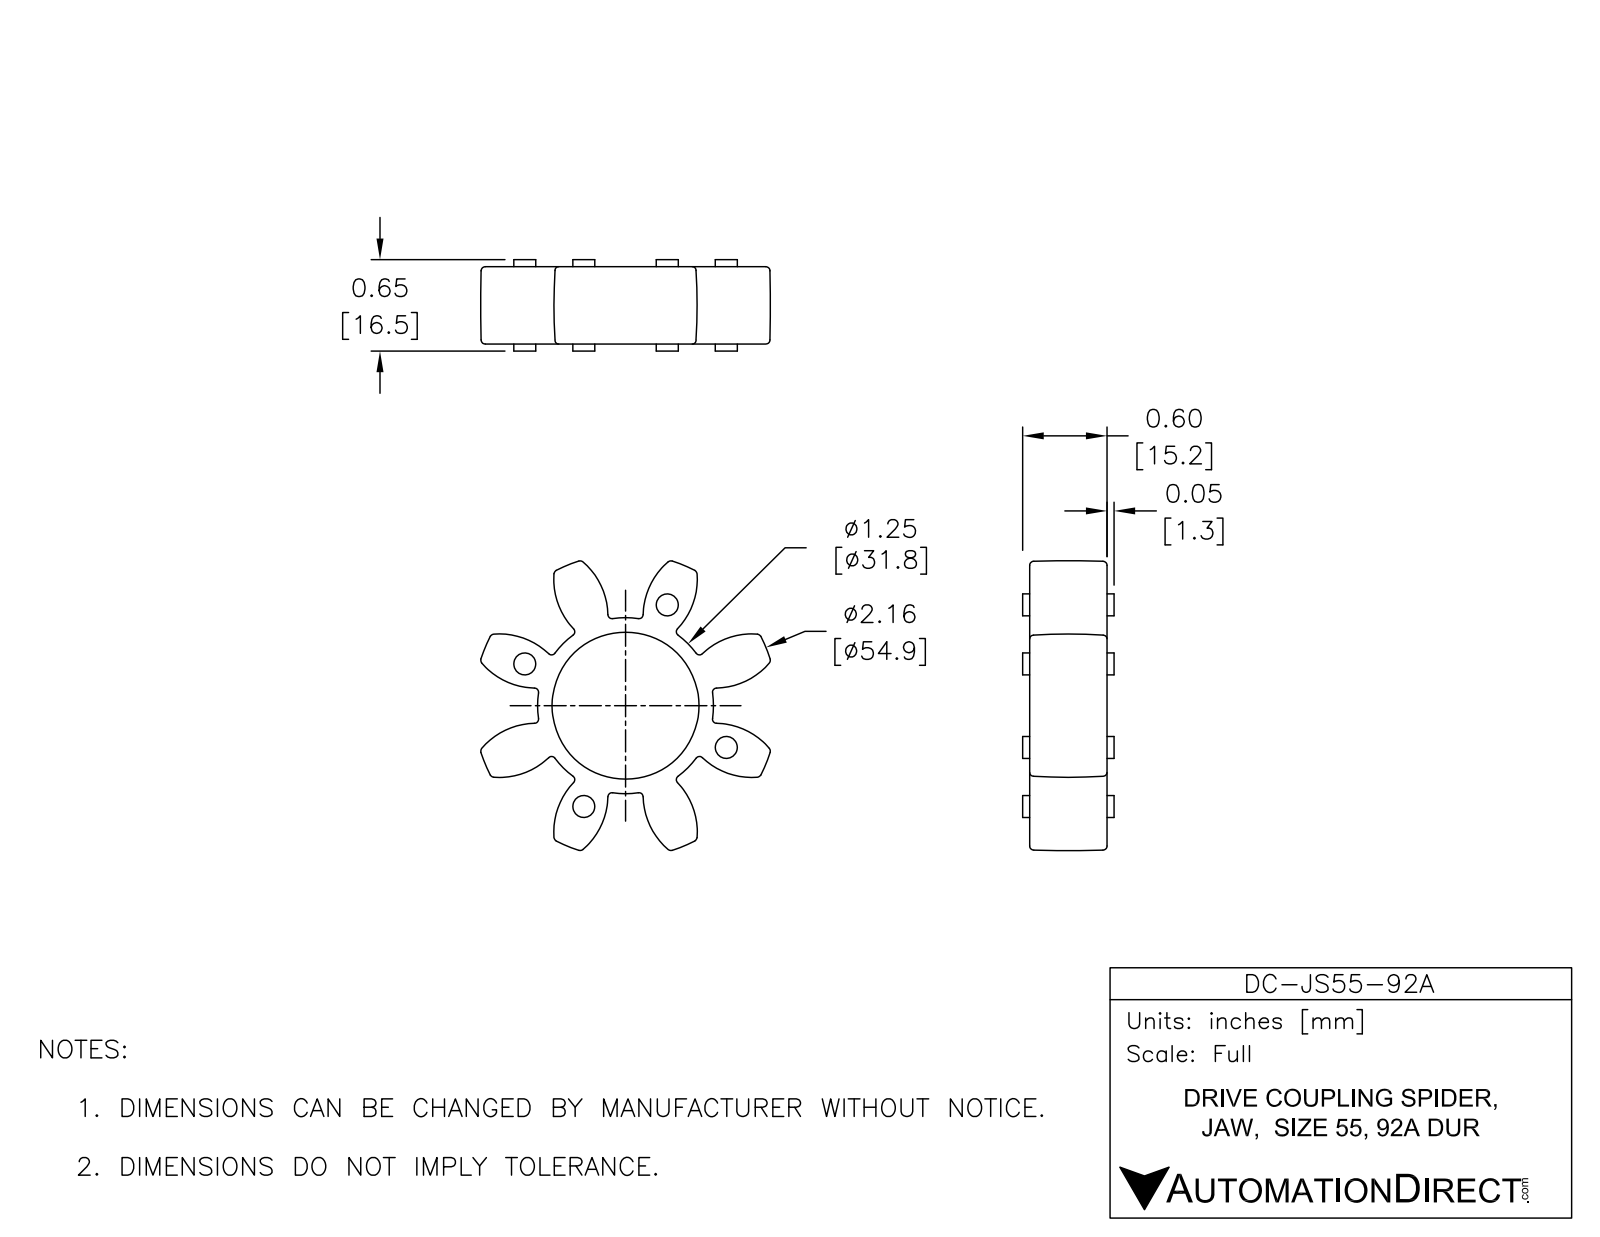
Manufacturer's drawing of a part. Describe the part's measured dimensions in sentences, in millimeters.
The part is named "DC-JS55-92A". Its 3-D file was written by "SolidWorks 2015 (AUTOMOTIVE_DESIGN)". It is 1 solid with 258 faces: 10 planar, 56 cylindrical and 192 other. Overall it measures 52.11 by 52.11 by 16.51 millimeters. Its volume is 12 424 cubic millimeters and its surface area 6 712 square millimeters. Round holes: 1 of diameter 26.54. Round bosses or shafts: 8 of diameter 3.96. Partial cylindrical surfaces (rounded edges, fillets, slot ends): 32 of radius 0.75. The main face-to-face distances are 13.98, 1.27, 15.25, 16.52.
